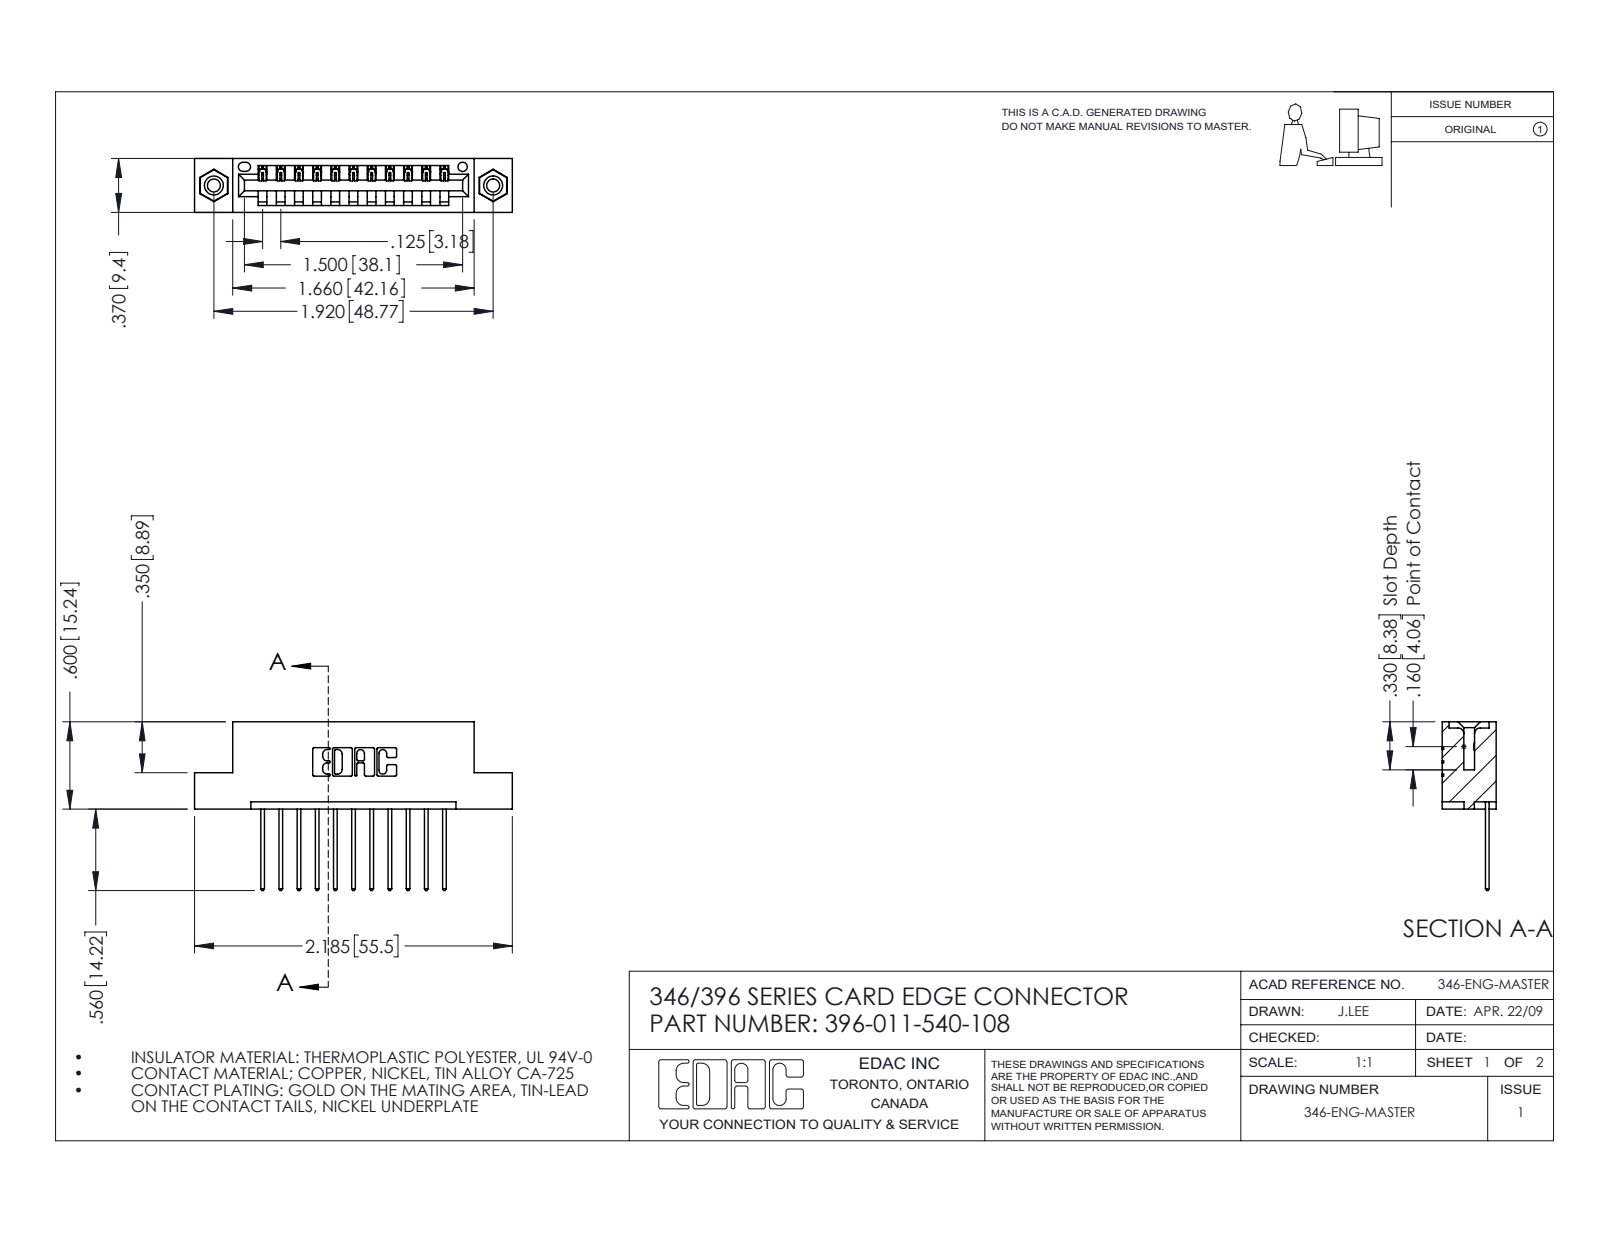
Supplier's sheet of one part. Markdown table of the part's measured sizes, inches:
| quantity | value |
| --- | --- |
| part name | 346 Part_Flush Mounting Lugs - 0.156 Dia-TI; 345-292-001_345-293-140; 396-011-540-108; 345-250-001_345-250-003-102 |
| STEP written by | SolidWorks 2016 (CONFIG_CONTROL_DESIGN) |
| units | inches |
| bodies | 14 solids, 820 faces (548 planar, 256 cylindrical, 16 other) |
| overall size | 2.185 × 1.16 × 0.37 |
| volume | 0.312 in³ |
| surface area | 9.578 in² |
| round holes (diameter × count) | 0.089 × 2, 0.125 × 2, 0.156 × 2, 0.064 × 1 |
| round bosses / shafts (diameter × count) | 0.155 × 2 |
| partial cylindrical surfaces (radius × count) | 0.006 × 22, 0.01 × 22, 0.01 × 22, 0.007 × 6, 0.031 × 6, 0.026 × 3, 0.031 × 2, 0.04 × 2 |
| main face-to-face distances | 0.25, 0.048, 0.322, 0.37, 0.072, 0.298, 0.025, 0.148, 0.222, 0.1 |
| hole center spacings | 0.246, 1.715, 1.92 |
